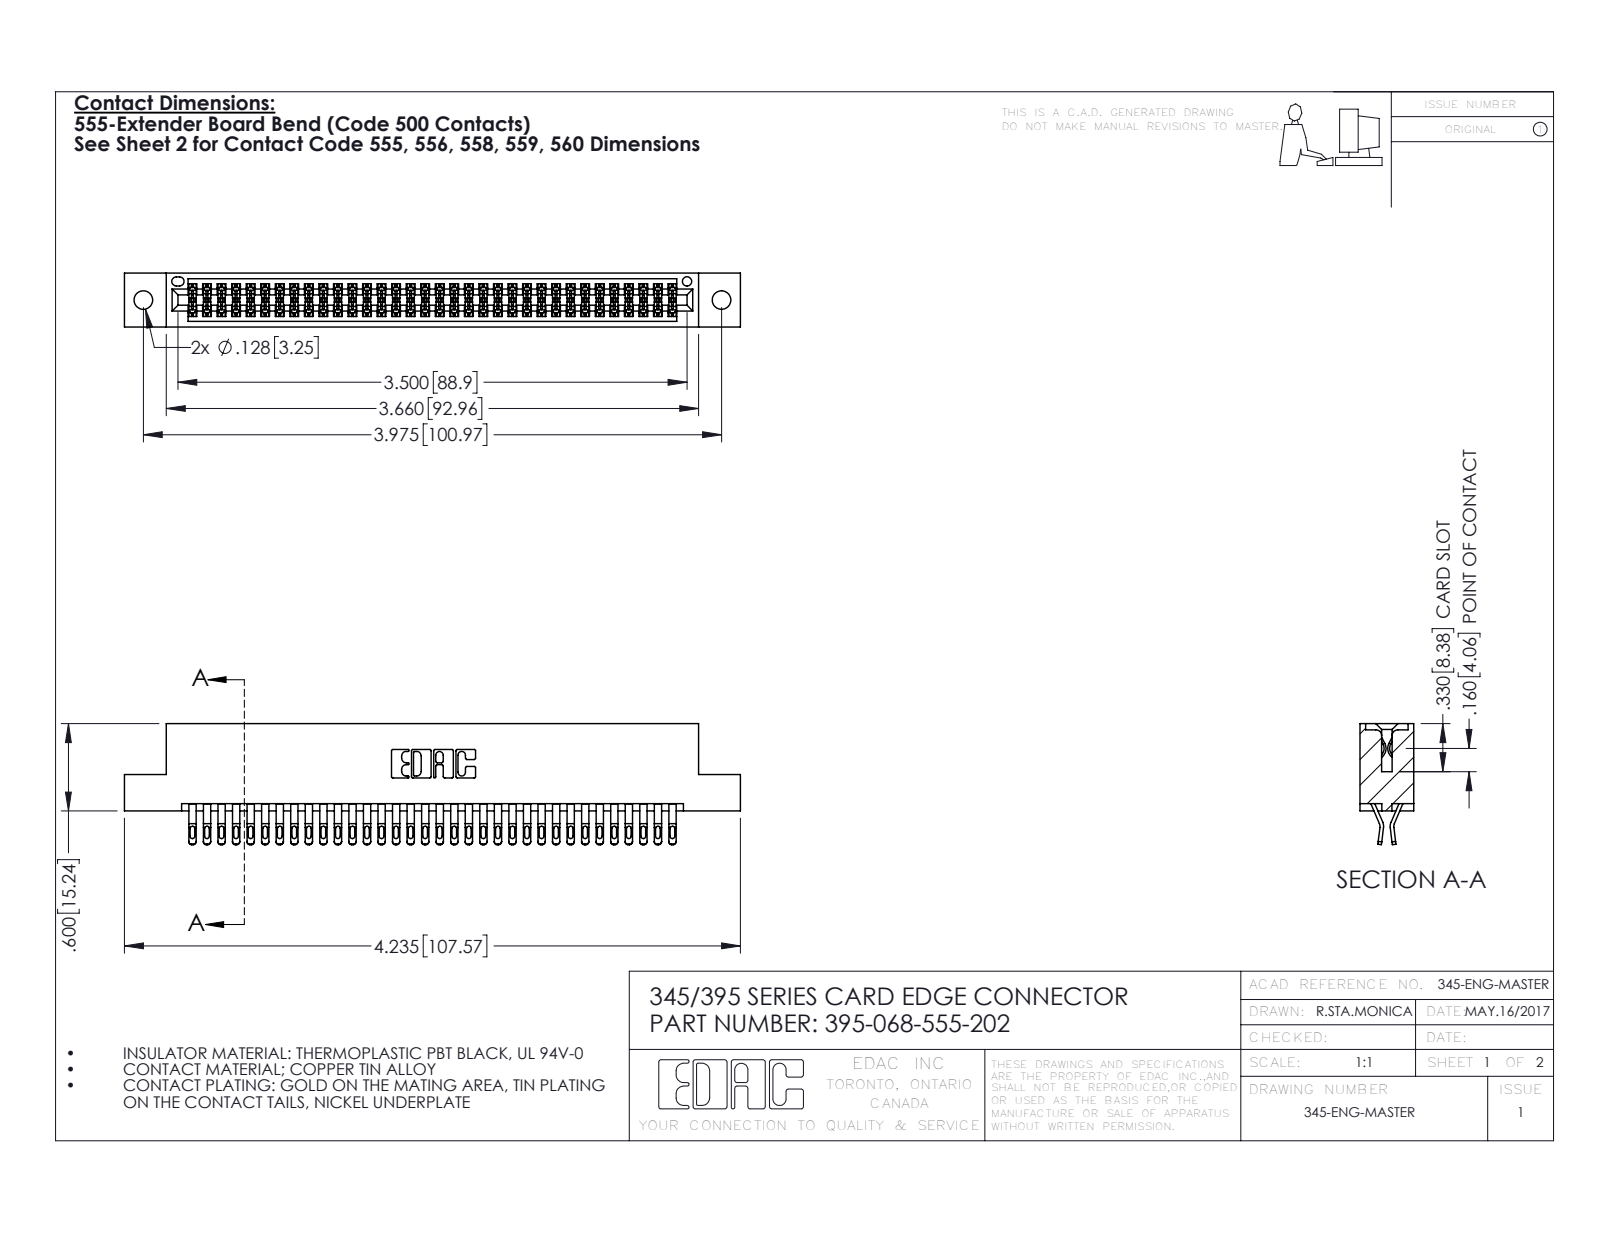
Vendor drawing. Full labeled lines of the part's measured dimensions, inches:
Part name (STEP PRODUCT): 345 Part_Flush Mounting Lugs - 0.128 Dia; 395-068-555-202; 345-292-001_555 Tail
STEP written by: SolidWorks 2016 (CONFIG_CONTROL_DESIGN)
Units: inches
Bodies: 69 solids, 3934 faces (2188 planar, 1746 cylindrical, 0 other)
Overall size (bounding box): 4.235 × 0.832 × 0.37
Volume: 0.643 in³ · Surface area: 24.54 in²
Round holes (diameter × count): ⌀0.128 ×2, ⌀0.064 ×1
Partial cylindrical surfaces — rounded edges, fillets, slot ends (radius × count): R0.016 ×170, R0.02 ×136, R0.006 ×102, R0.01 ×22, R0.007 ×6, R0.031 ×6, R0.026 ×3, R0.01 ×2
Main face-to-face distances: 0.298, 0.072, 0.2, 0.37, 0.025, 0.098, 0.272, 0.225, 0.175, 0.149
Hole centre spacings: 0.27, 3.74, 3.975
